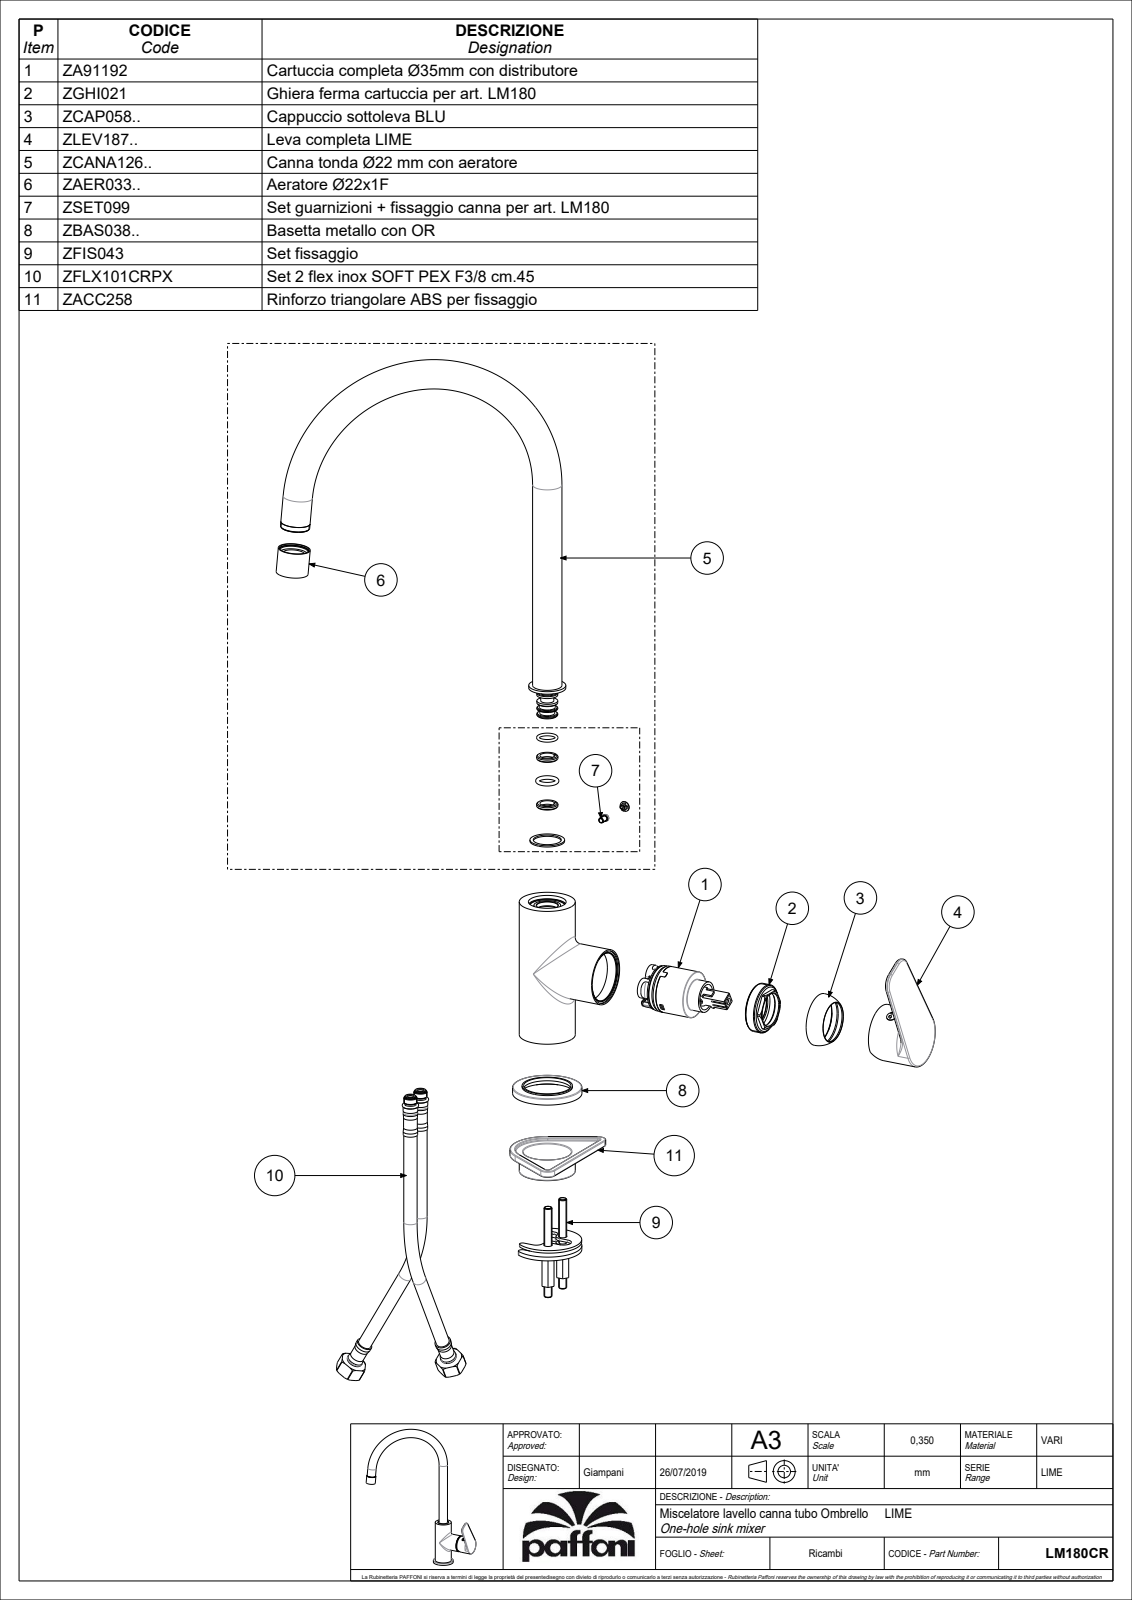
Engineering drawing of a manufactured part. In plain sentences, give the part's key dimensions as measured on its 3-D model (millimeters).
The part is named "LM180CR". Its 3-D file was written by "CREO PARAMETRIC BY PTC INC, 2020044 (CONFIG_CONTROL_DESIGN)". It is 6 solids with 2656 faces: 1947 planar, 446 cylindrical and 263 other. Overall it measures 379 by 294.98 by 75.69 millimeters. Its volume is 153 312 cubic millimeters and its surface area 163 019 square millimeters. Round holes: 3 of diameter 5.5, 3 of diameter 9, 3 of diameter 12, 2 of diameter 3, 2 of diameter 6, 2 of diameter 6.5, 2 of diameter 7, 2 of diameter 8, 2 of diameter 9.5, 2 of diameter 19.6, 2 of diameter 38, 1 of diameter 3.3. Round bosses or shafts: 3 of diameter 42, 3 of diameter 12, 2 of diameter 22, 2 of diameter 14, 2 of diameter 10.5, 2 of diameter 10, 2 of diameter 9, 2 of diameter 7.6. Partial cylindrical surfaces (rounded edges, fillets, slot ends): 62 of radius 0.5, 22 of radius 1, 21 of radius 0.3, 14 of radius 0.54, 14 of radius 3, 4 of radius 4.5, 3 of radius 2, 3 of radius 7.25. The main face-to-face distances are 2, 3.5, 34, 2.5, 1, 36, 5, 35.5, 70, 67.5. The hole center spacings are 13.04, 0.7, 8.51, 8.6, 9.3, 12.98, 13.21, 13.51.
